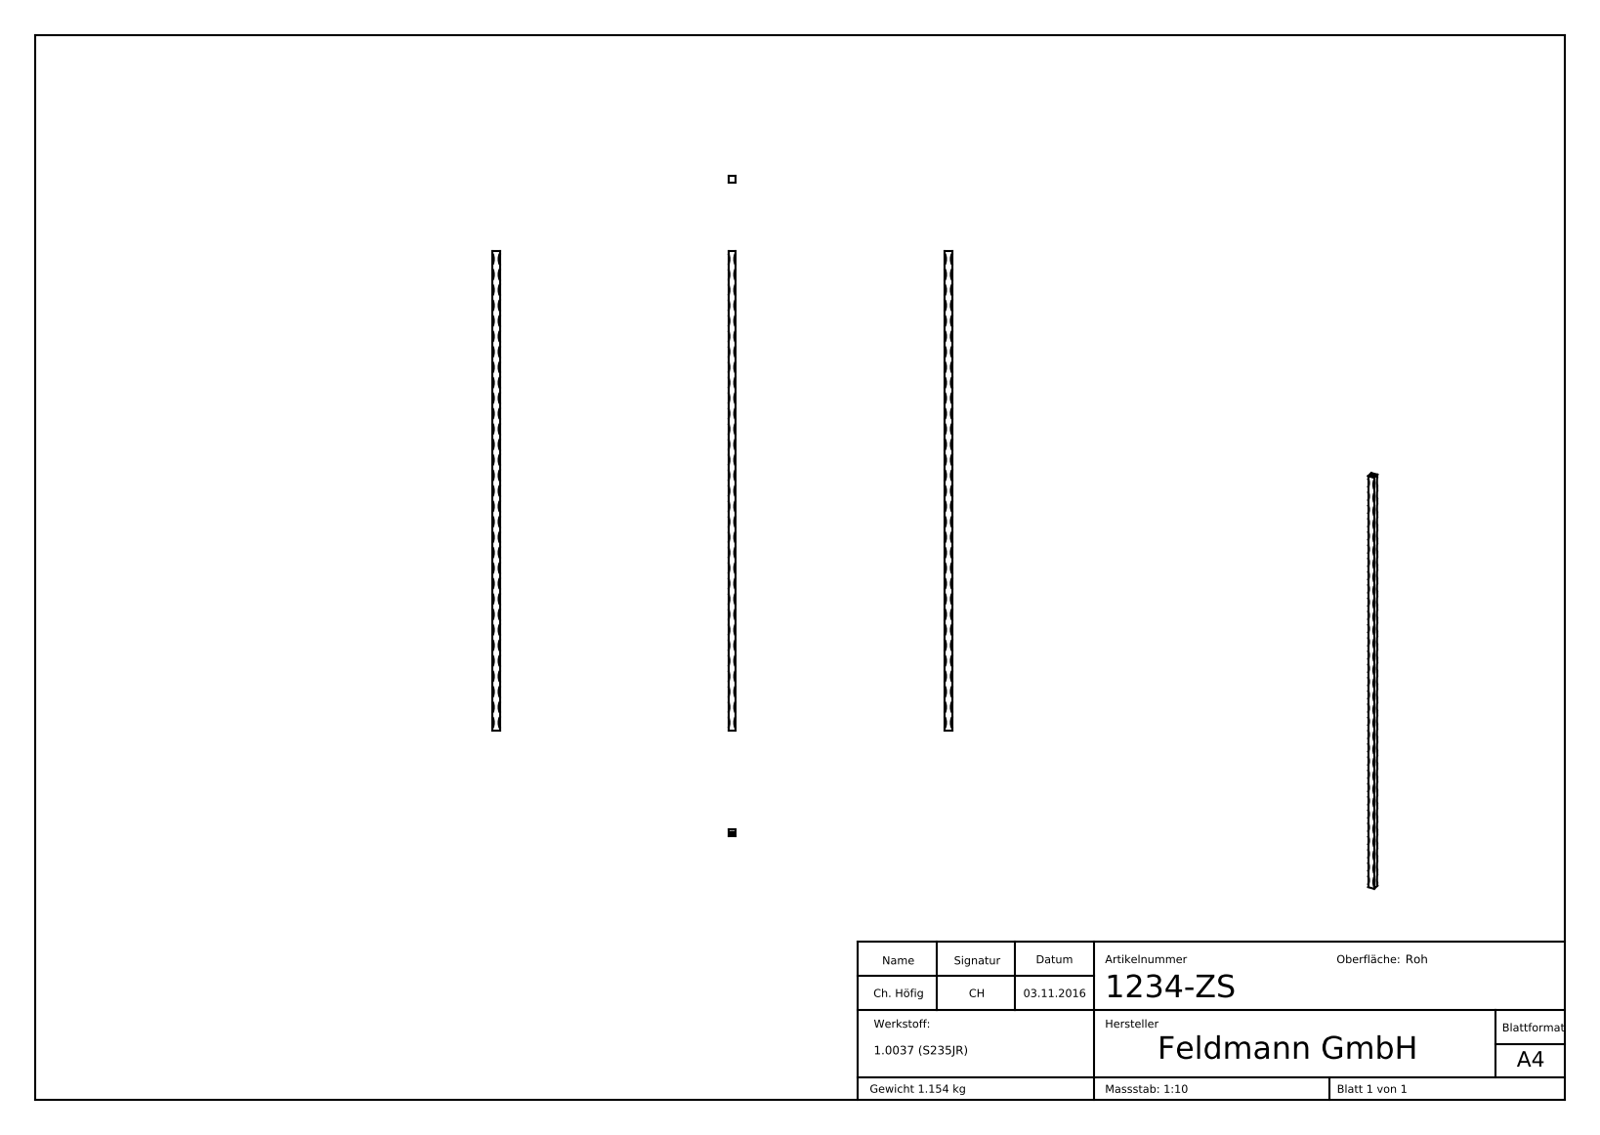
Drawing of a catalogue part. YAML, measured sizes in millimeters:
part_name: "1234-ZS"
step_written_by: "SolidWorks 2015 (CONFIG_CONTROL_DESIGN)"
units: millimeters
bodies: {solids: 1, faces: 328, planar: 121, cylindrical: 0, other: 207}
overall_size: [900, 13, 13]
volume: 147897
surface_area: 45798
face_to_face_distances: [13, 900, 899.9, 3.27, 1.5, 6.5, 1.77, 3.36, 0.39, 3.39]
